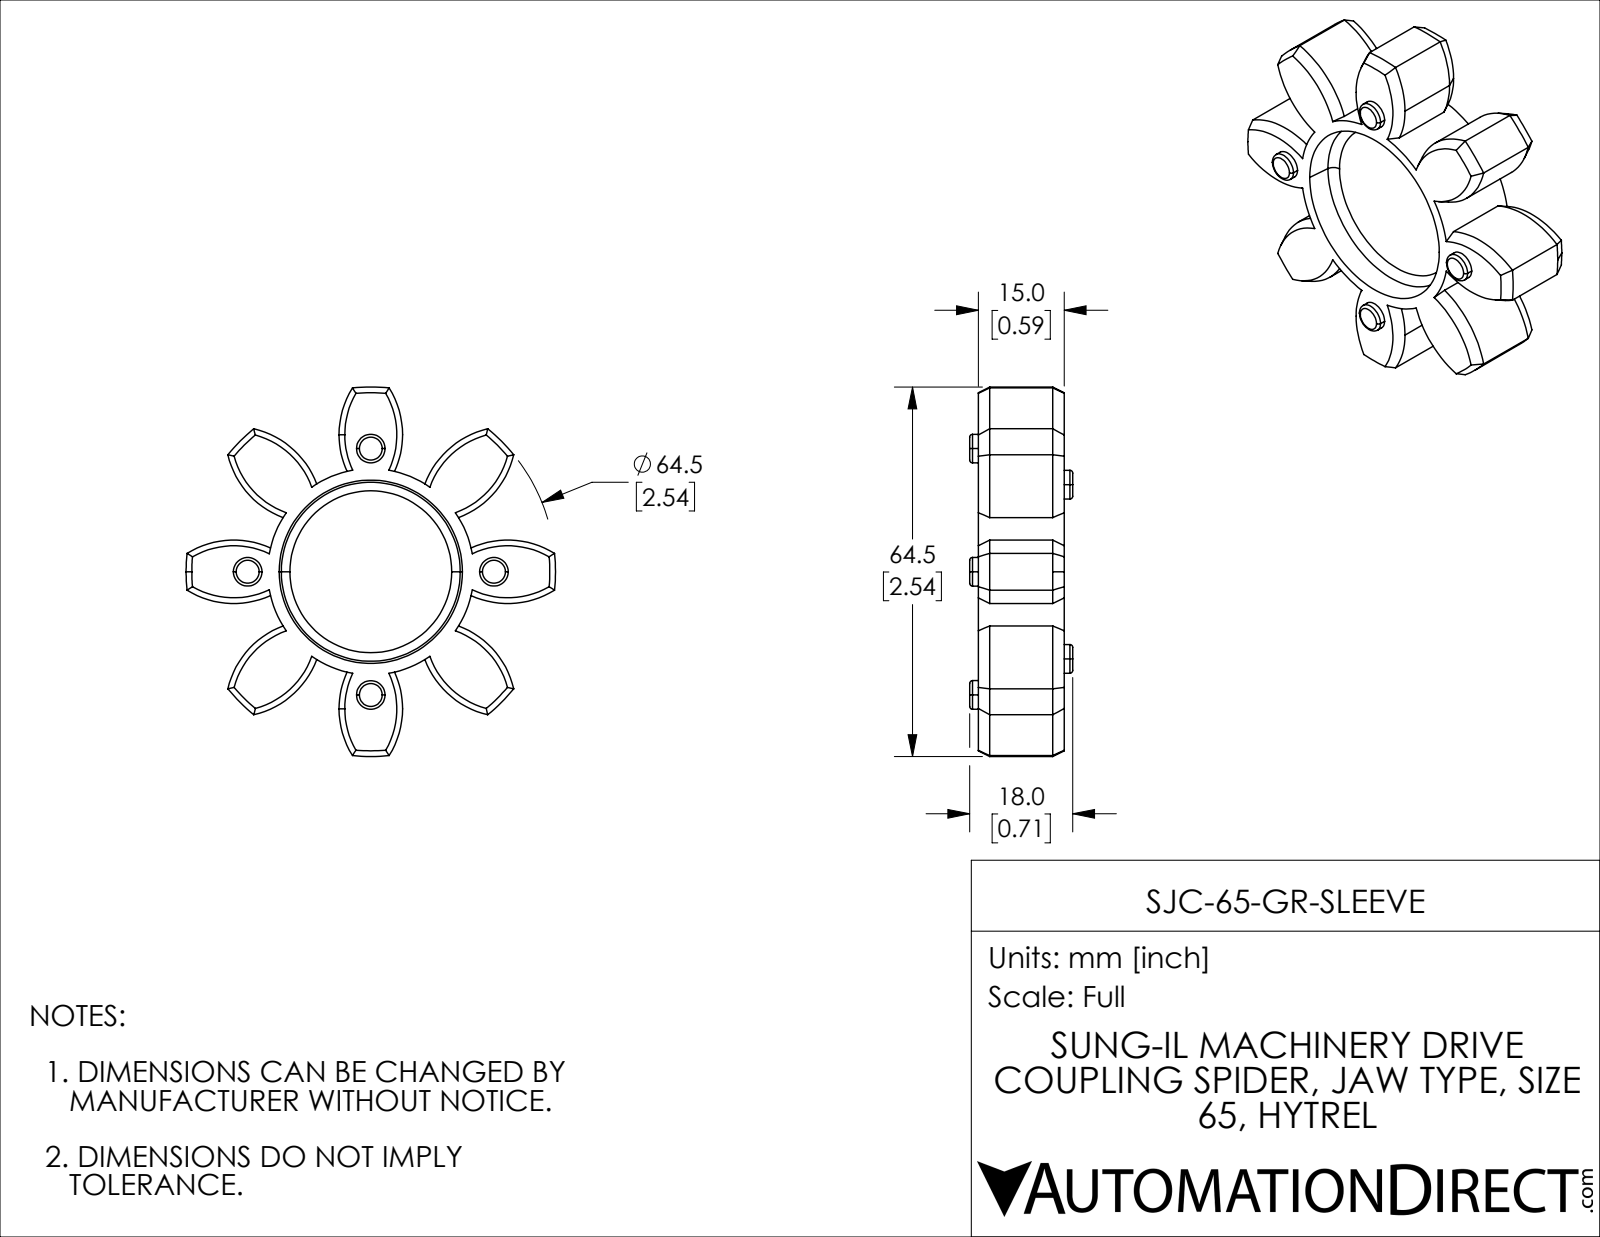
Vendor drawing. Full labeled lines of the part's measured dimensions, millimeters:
Part name (STEP PRODUCT): SJC-65-GR-SLEEVE
STEP written by: SolidWorks 2021 (CONFIG_CONTROL_DESIGN)
Units: millimetres
Bodies: 1 solid, 141 faces (12 planar, 51 cylindrical, 78 other)
Overall size (bounding box): 64.5 × 64.5 × 18
Volume: 23 398 mm³ · Surface area: 10 008 mm²
Round bosses / shafts (diameter × count): ⌀5 ×8
Partial cylindrical surfaces — rounded edges, fillets, slot ends (radius × count): R15.45 ×8, R18 ×1, R32.25 ×1
Main face-to-face distances: 5.5, 9.5, 15, 4, 1.5, 7, 11, 16.5, 18
